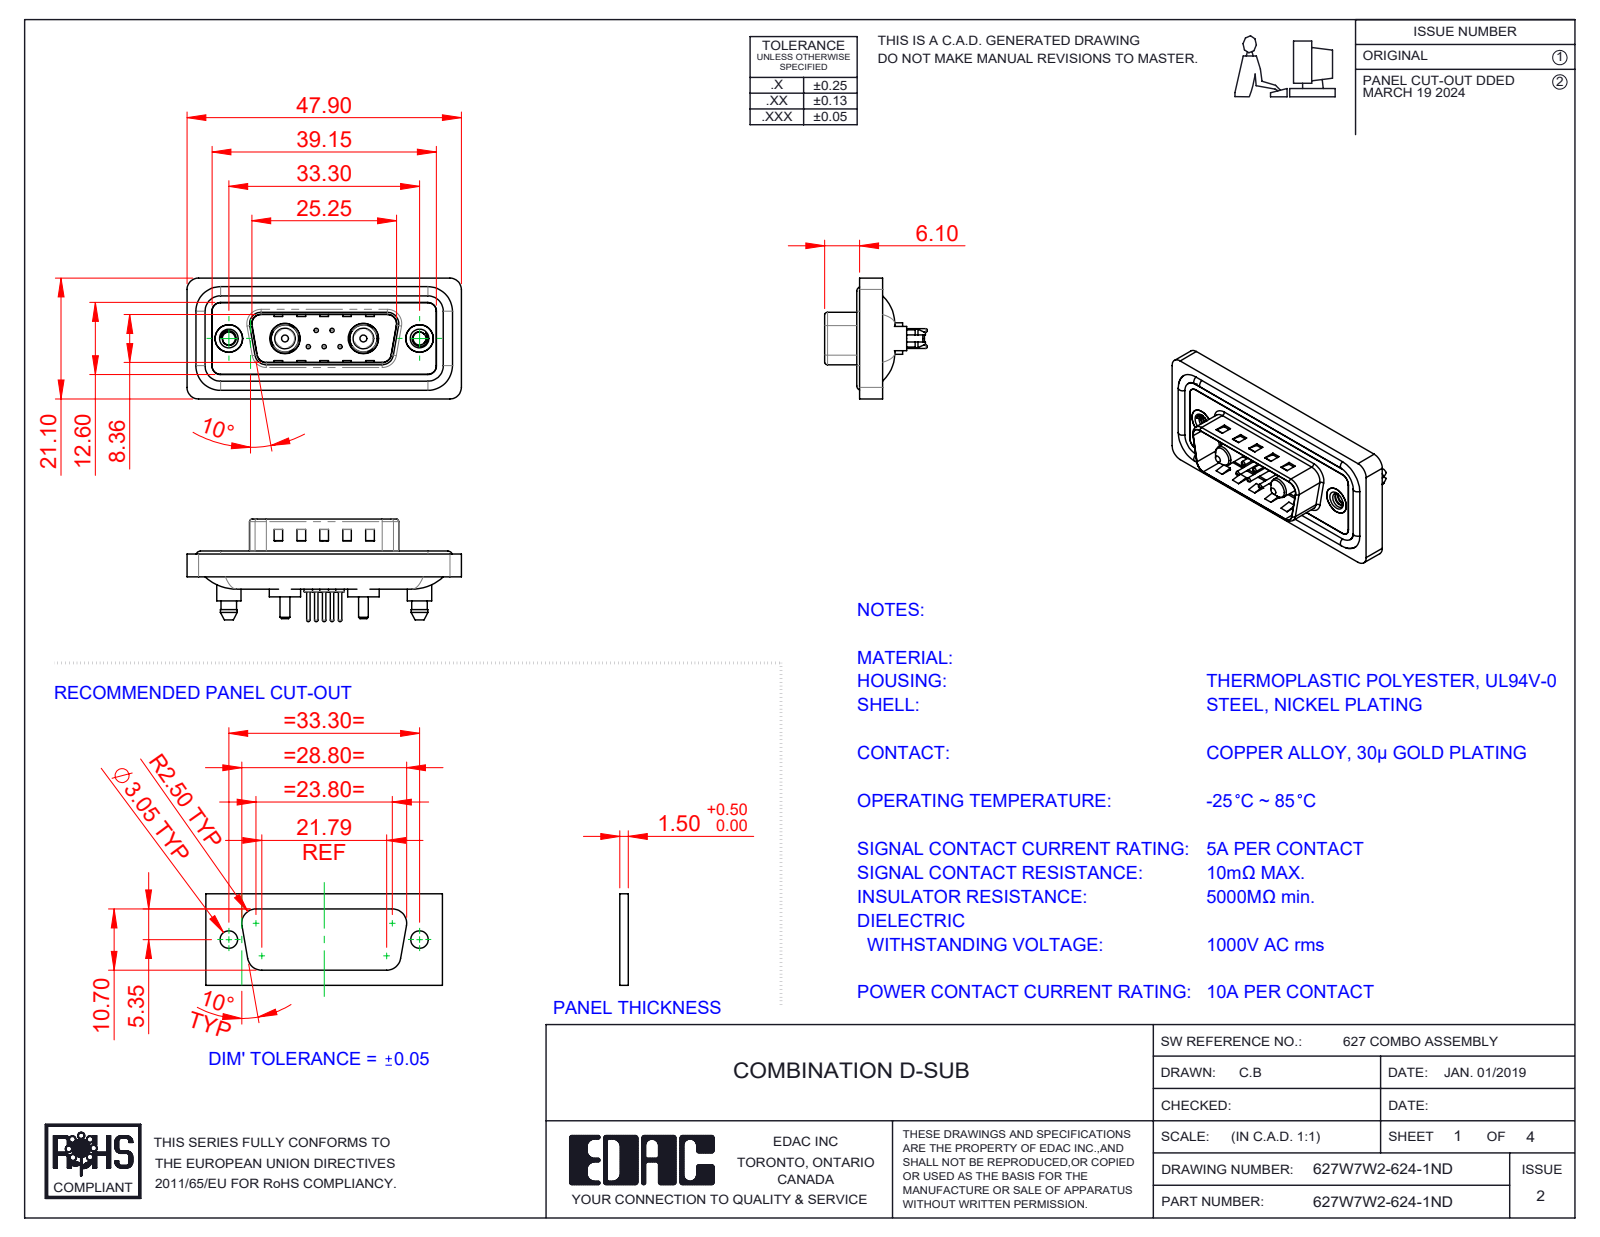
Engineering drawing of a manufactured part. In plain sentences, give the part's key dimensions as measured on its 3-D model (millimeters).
The part is named "627Combo Waterproof Housing_15 Contacts; Power Pin_10A S; 627Combo Contact Row 2_24; 627Combo Shell Rear_15 Contacts (+6 more)". Its 3-D file was written by "SolidWorks 2023 (CONFIG_CONTROL_DESIGN)". It is 16 solids with 768 faces: 248 planar, 332 cylindrical and 188 other. Overall it measures 47.9 by 21.1 by 17.9 millimeters. Its volume is 5 622 cubic millimeters and its surface area 9 104 square millimeters. Round holes: 5 of diameter 0.75, 5 of diameter 1.6, 5 of diameter 2, 2 of diameter 2.26, 2 of diameter 4, 2 of diameter 4.8, 2 of diameter 4.85, 2 of diameter 5, 2 of diameter 5.3. Round bosses or shafts: 5 of diameter 1.5, 5 of diameter 0.6, 4 of diameter 1.6, 2 of diameter 5.5, 2 of diameter 5.4, 2 of diameter 5.2, 2 of diameter 4.9, 2 of diameter 4.75. Partial cylindrical surfaces (rounded edges, fillets, slot ends): 28 of radius 1.5, 20 of radius 2, 10 of radius 1.6, 8 of radius 0.5, 4 of radius 0.25, 4 of radius 0.6, 4 of radius 0.65, 4 of radius 0.9. The main face-to-face distances are 0.4, 1.1, 1.5, 1.6, 0.5, 3.1, 2.9, 4, 0.7, 0.82. The hole center spacings are 3.16, 2.77, 9.8, 23.5, 4.31, 4.33, 5.03, 5.04.
